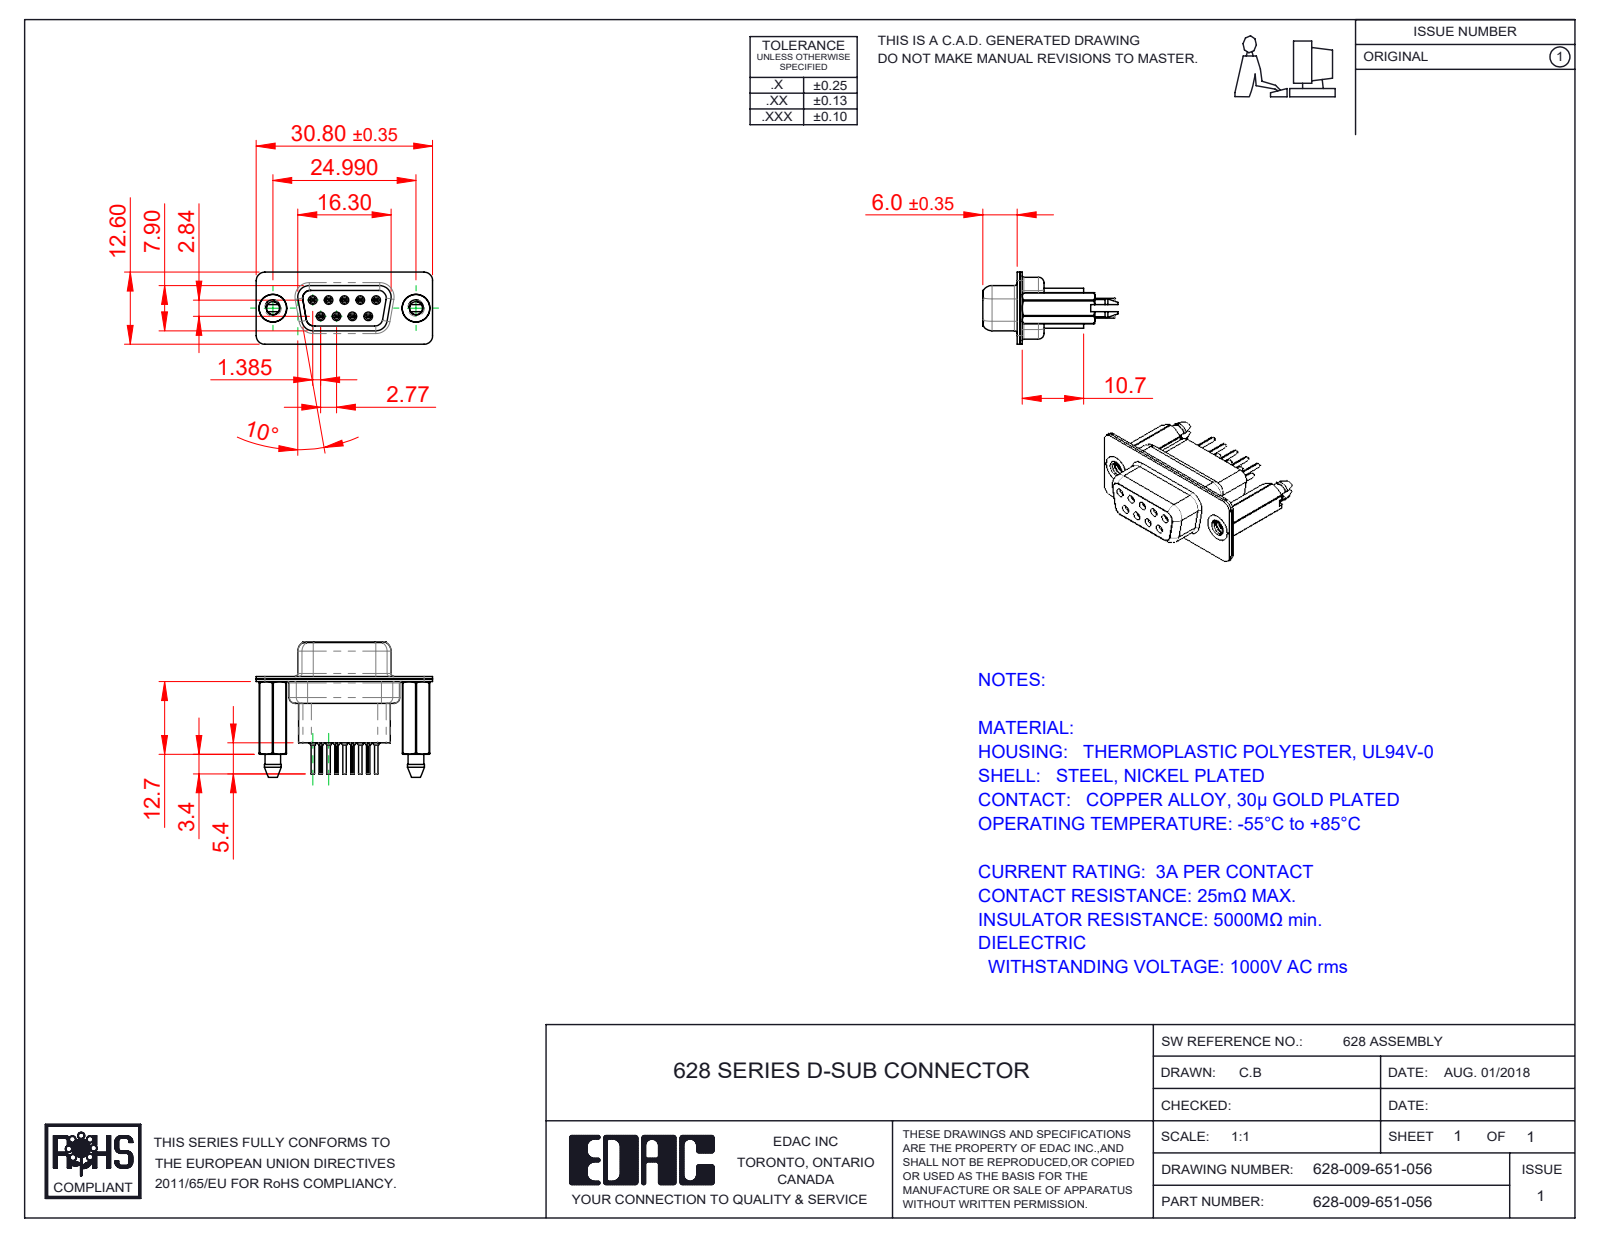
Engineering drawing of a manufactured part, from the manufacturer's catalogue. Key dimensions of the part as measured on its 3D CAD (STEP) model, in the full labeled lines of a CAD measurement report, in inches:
Part name (STEP PRODUCT): 628 Contact Row 2_51; 628-009-651-056; 628 Shell Rear_09 Contacts; 628 Housing_09 HP (+3 more)
STEP written by: SolidWorks 2020 (CONFIG_CONTROL_DESIGN)
Units: inches
Bodies: 14 solids, 1460 faces (378 planar, 466 cylindrical, 616 other)
Overall size (bounding box): 1.213 × 0.929 × 0.496
Volume: 0.156 in³ · Surface area: 9.252 in²
Round holes (diameter × count): ⌀0.008 ×9, ⌀0.031 ×9, ⌀0.035 ×9, ⌀0.043 ×9, ⌀0.063 ×9, ⌀0.067 ×5, ⌀0.089 ×2, ⌀0.157 ×2, ⌀0.159 ×2, ⌀0.191 ×2
Round bosses / shafts (diameter × count): ⌀0.079 ×9, ⌀0.059 ×9, ⌀0.047 ×9, ⌀0.024 ×9, ⌀0.195 ×2, ⌀0.189 ×2
Partial cylindrical surfaces — rounded edges, fillets, slot ends (radius × count): R0.059 ×19, R0.004 ×18, R0.079 ×12, R0.011 ×9, R0.053 ×6, R0.063 ×6, R0.01 ×4, R0.02 ×4
Main face-to-face distances: 0.018, 0.016, 0.035, 0.335, 0.26, 0.075, 0.055, 0.187, 0.276, 0.421
Hole centre spacings: 0.124, 0.109, 0.218, 0.198, 0.198, 0.327, 0.294, 0.295
